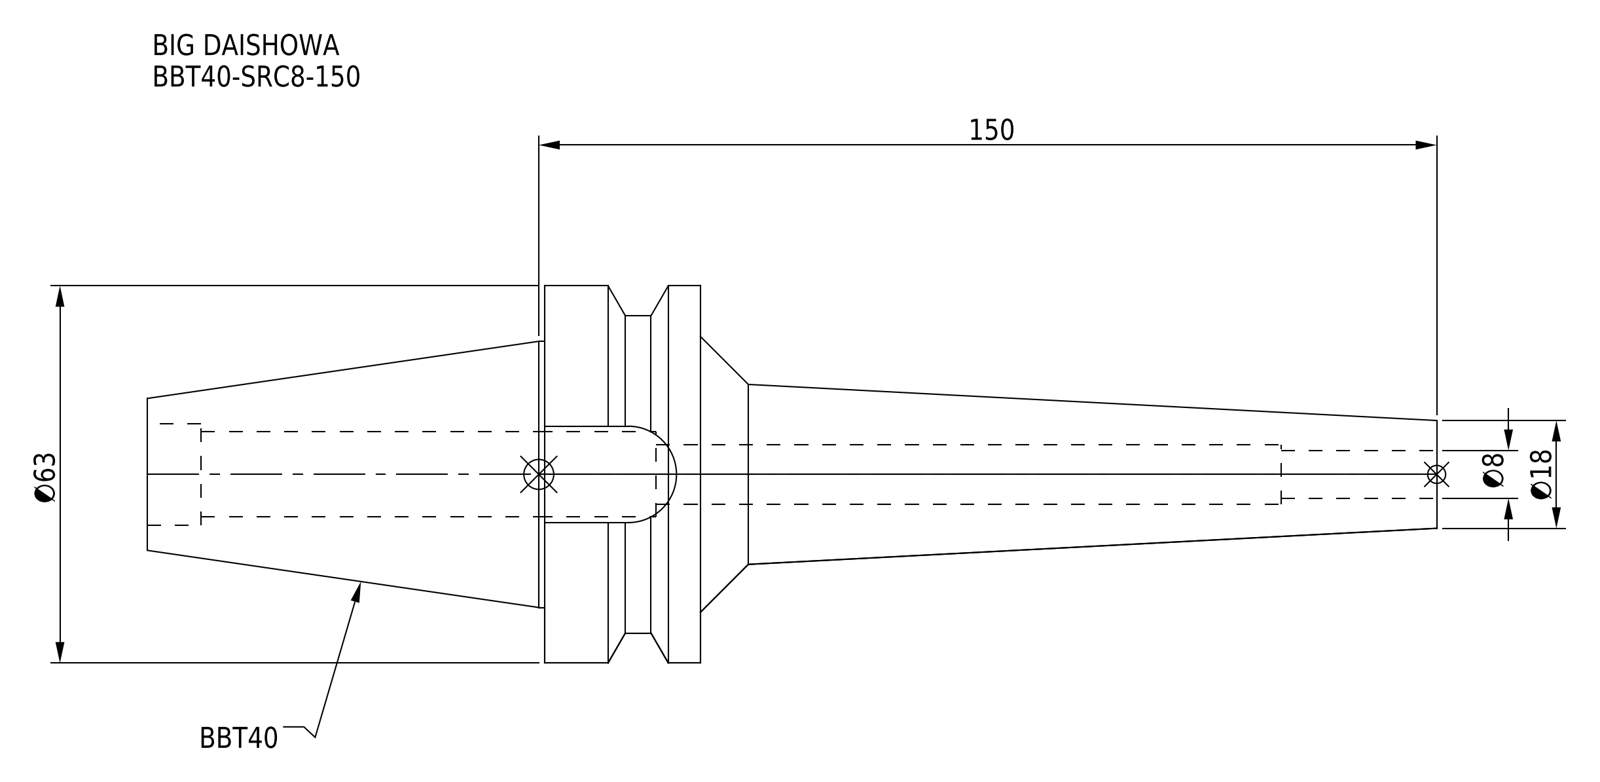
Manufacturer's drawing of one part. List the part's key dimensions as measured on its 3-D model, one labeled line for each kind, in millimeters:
Part name (STEP PRODUCT): BBT40-SRC8-150
STEP written by: CREO PARAMETRIC BY PTC INC, 2016380 (AUTOMOTIVE_DESIGN)
Units: millimetres
Bodies: 1 solid, 43 faces (13 planar, 20 cylindrical, 10 other)
Overall size (bounding box): 215.4 × 63 × 63
Volume: 174 462 mm³ · Surface area: 35 149 mm²
Round holes (diameter × count): ⌀8 ×1, ⌀10 ×1, ⌀14.2 ×1, ⌀17 ×1
Round bosses / shafts (diameter × count): ⌀63 ×1, ⌀53 ×1, ⌀44.45 ×1
Partial cylindrical surfaces — rounded edges, fillets, slot ends (radius × count): R8.05 ×1
Main face-to-face distances: 26, 45, 92.4, 66.4, 123, 149, 215.4, 16.1, 130.4, 7.4
